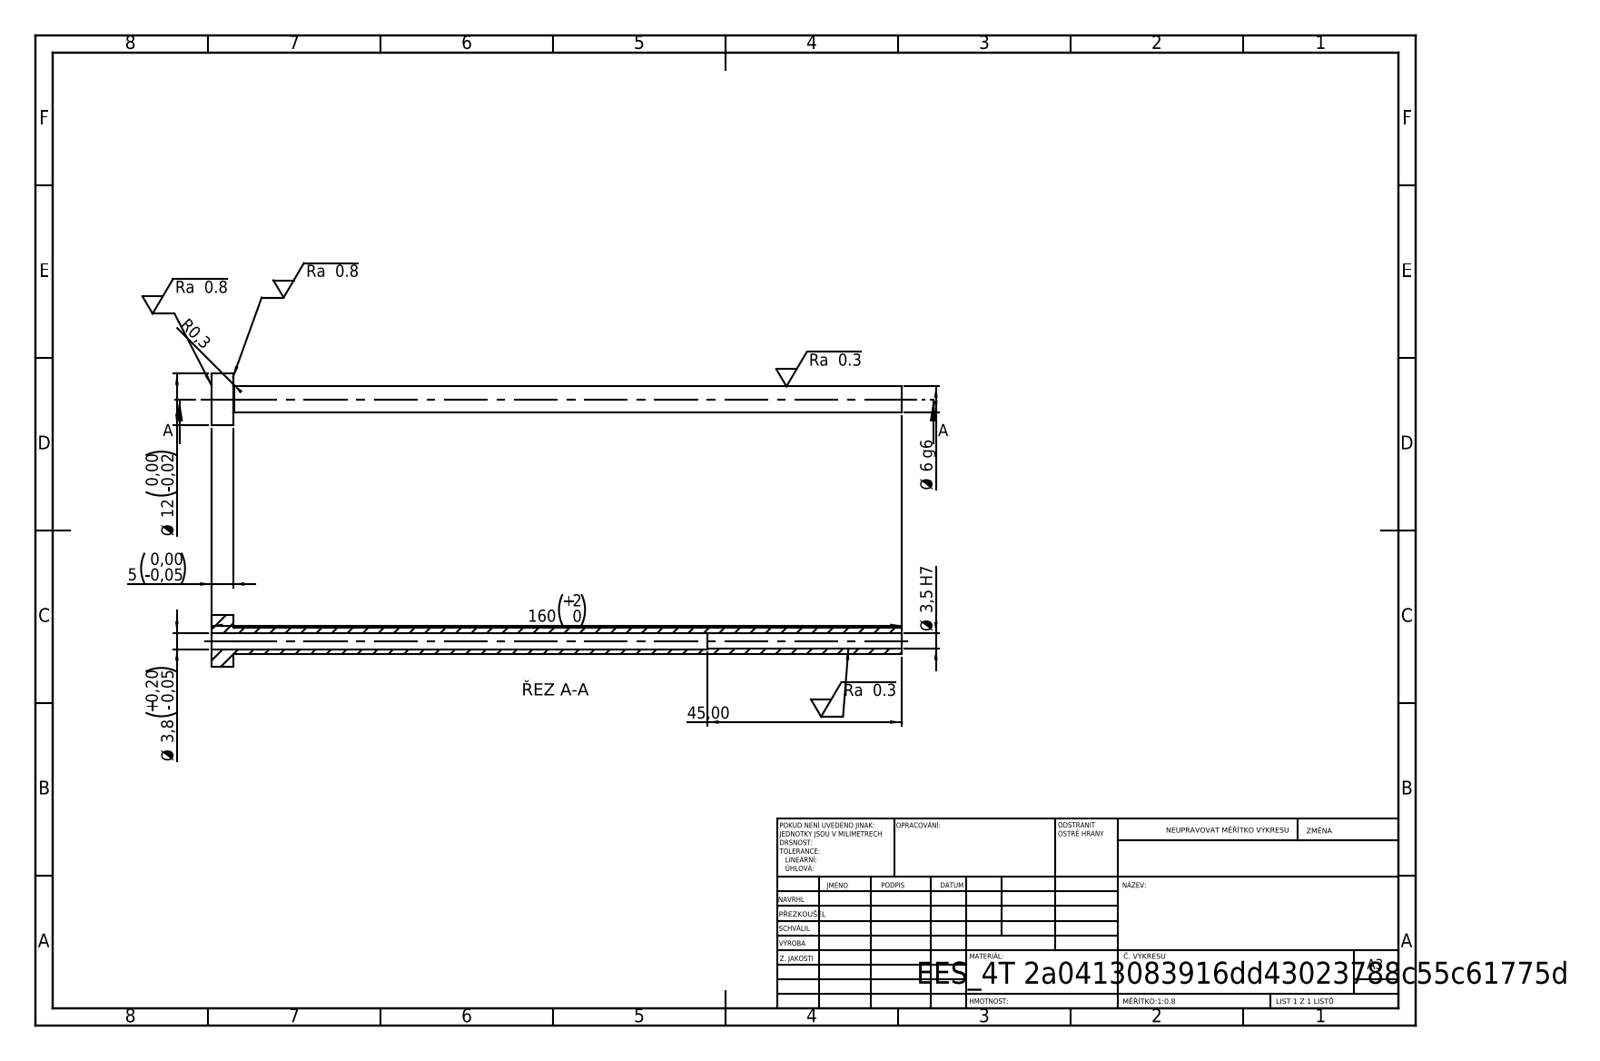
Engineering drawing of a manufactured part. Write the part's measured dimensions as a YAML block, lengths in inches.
step_written_by: "SolidWorks 2019 (CONFIG_CONTROL_DESIGN)"
units: inches
bodies: {solids: 1, faces: 14, planar: 4, cylindrical: 8, other: 2}
overall_size: [6.299, 0.472, 0.472]
volume: 0.196
surface_area: 8.032
round_holes:
  - {diameter: 0.138, count: 1}
  - {diameter: 0.15, count: 1}
round_bosses_or_shafts:
  - {diameter: 0.472, count: 1}
  - {diameter: 0.236, count: 1}
face_to_face_distances: [0.197, 6.299, 6.102, 4.528, 4.331, 1.772]
